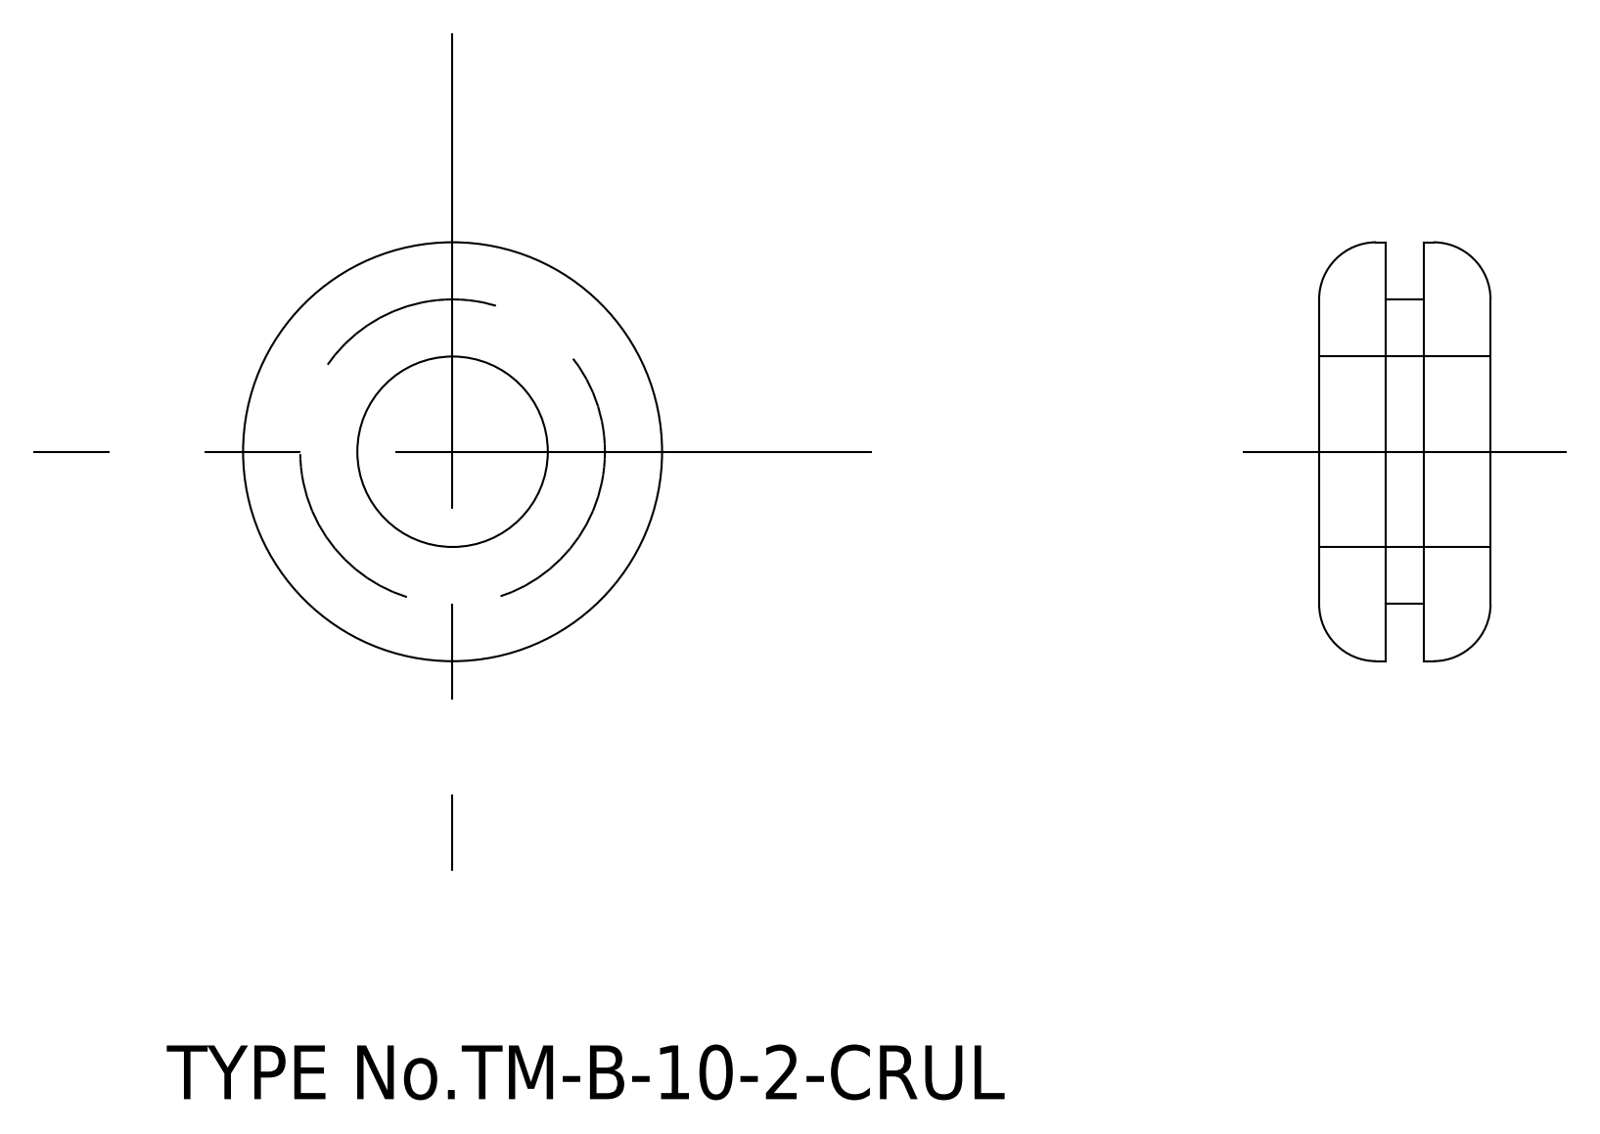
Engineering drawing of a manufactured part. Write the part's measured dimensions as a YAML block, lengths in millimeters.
step_written_by: "spGate 15.6.1 (AUTOMOTIVE_DESIGN)"
units: millimeters
bodies: {solids: 1, faces: 16, planar: 4, cylindrical: 8, other: 4}
overall_size: [22, 22, 9]
volume: 2106
surface_area: 1643
round_holes:
  - {diameter: 10, count: 1}
round_bosses_or_shafts:
  - {diameter: 22, count: 1}
  - {diameter: 16, count: 1}
face_to_face_distances: [3.5, 5.5, 2, 9]
